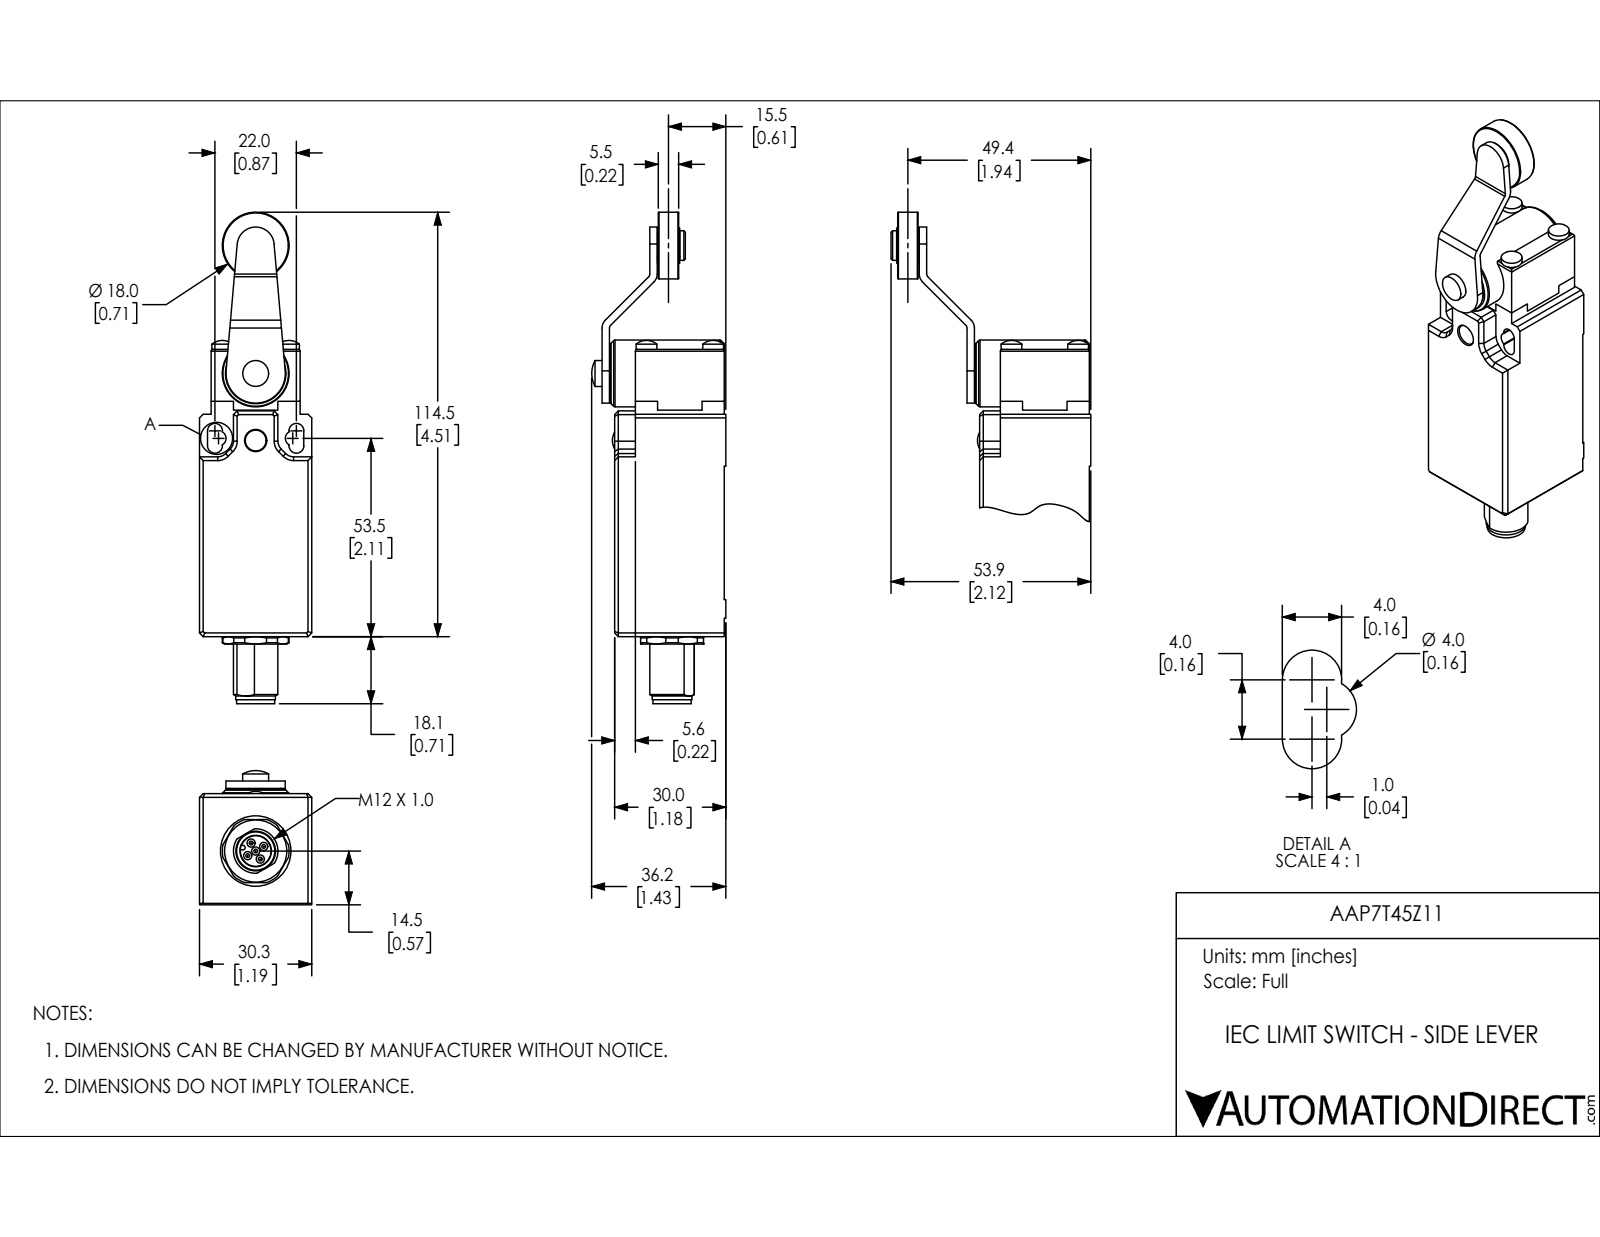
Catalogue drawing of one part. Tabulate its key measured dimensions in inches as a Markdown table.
| quantity | value |
| --- | --- |
| part name | AAP7T45Z11 |
| STEP written by | SolidWorks 2018 (AUTOMOTIVE_DESIGN) |
| units | inches |
| bodies | 4 solids, 344 faces (151 planar, 131 cylindrical, 62 other) |
| overall size | 5.22 × 1.425 × 1.193 |
| volume | 4.211 in³ |
| surface area | 28.79 in² |
| round holes (diameter × count) | 0.087 × 5, 0.236 × 1, 0.512 × 1, 0.551 × 1, 0.63 × 1 |
| round bosses / shafts (diameter × count) | 0.22 × 5, 0.055 × 5, 0.039 × 5, 0.709 × 2, 0.587 × 1, 0.531 × 1, 0.421 × 1, 0.406 × 1 |
| partial cylindrical surfaces (radius × count) | 0.079 × 6, 0.118 × 6, 0.02 × 4, 0.039 × 2, 0.024 × 1, 0.197 × 1, 0.236 × 1, 0.315 × 1 |
| main face-to-face distances | 1.193, 1.165, 0.124, 1.069, 0.945, 0.079, 2.406, 0.276, 1.181, 0.016 |
| hole center spacings | 0.098, 0.139, 0.196 |
